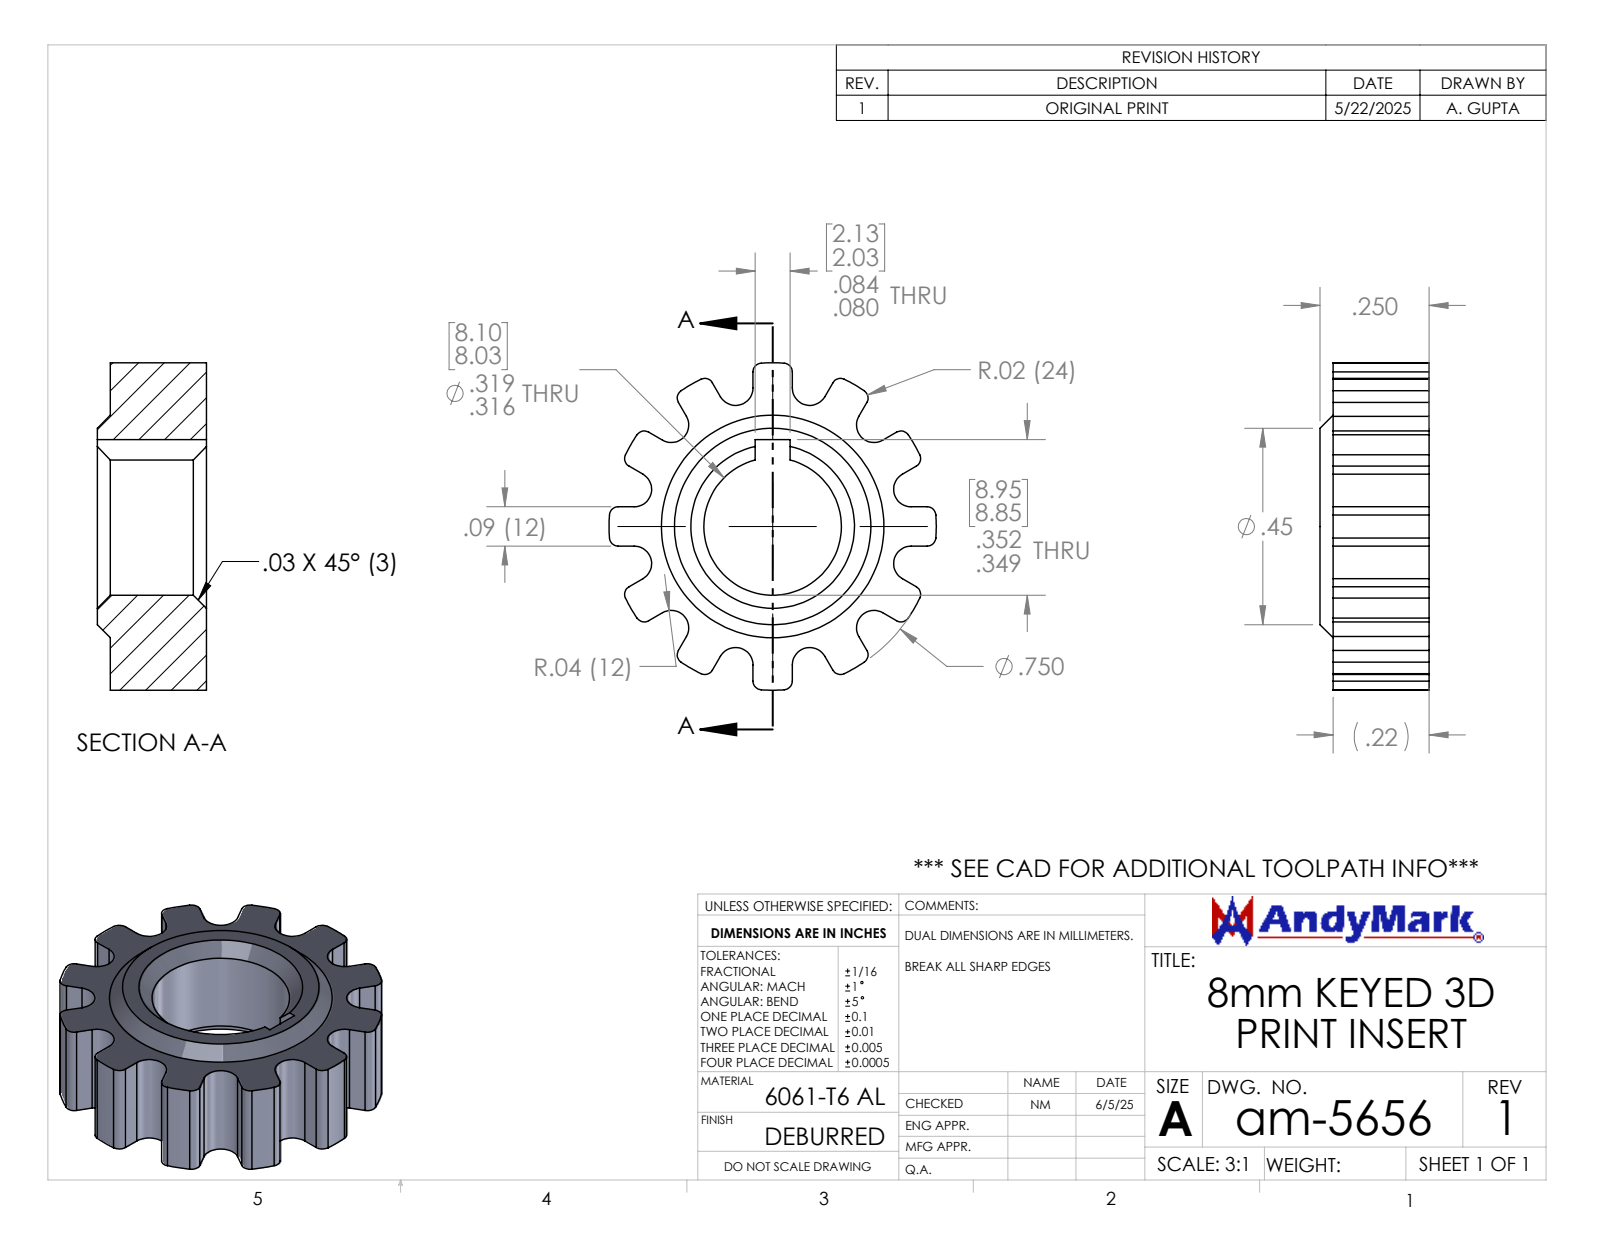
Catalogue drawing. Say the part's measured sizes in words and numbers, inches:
The part is named "am-5656 8mm Keyed 3D Print Insert". Its 3-D file was written by "SolidWorks 2024 (AUTOMOTIVE_DESIGN)". It is 1 solid with 98 faces: 30 planar, 60 cylindrical and 8 other. Overall it measures 0.75 by 0.75 by 0.25 inches. Its volume is 0.063 cubic inches and its surface area 1.581 square inches. Round holes: 1 of diameter 0.315. Partial cylindrical surfaces (rounded edges, fillets, slot ends): 24 of radius 0.02, 12 of radius 0.04, 1 of radius 0.375. The main face-to-face distances are 0.22, 0.09, 0.25, 0.03, 0.085, 0.244, 0.154, 0.08.
